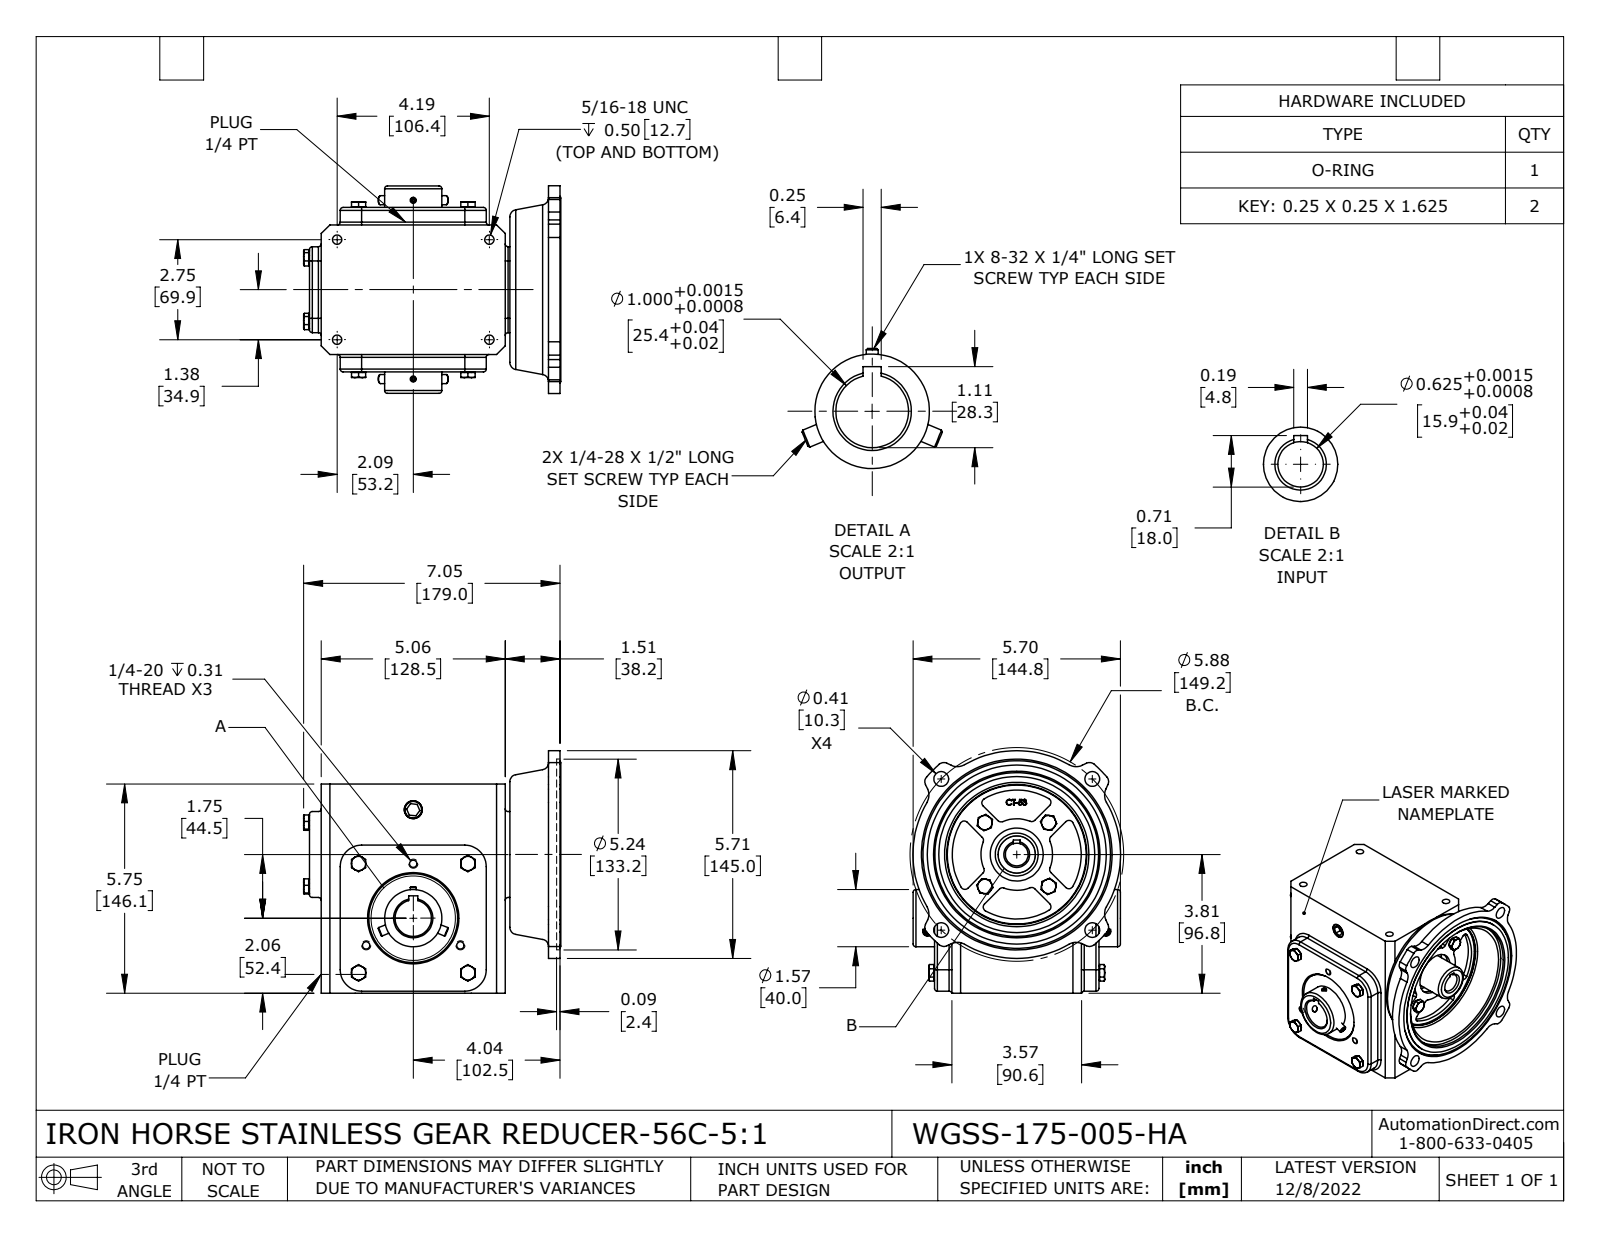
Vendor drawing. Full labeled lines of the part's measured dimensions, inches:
Part name (STEP PRODUCT): WGSS-175-005-HA
STEP written by: SolidWorks 2021 (CONFIG_CONTROL_DESIGN)
Units: inches
Bodies: 7 solids, 891 faces (390 planar, 231 cylindrical, 270 other)
Overall size (bounding box): 7.071 × 6.691 × 5.709
Volume: 127 in³ · Surface area: 281 in²
Round holes (diameter × count): ⌀0.213 ×4, ⌀0.257 ×4, ⌀0.406 ×4, ⌀0.201 ×3, ⌀0.136 ×2, ⌀0.625 ×1, ⌀0.866 ×1, ⌀1 ×1, ⌀1.102 ×1, ⌀1.457 ×1, ⌀1.575 ×1, ⌀3.819 ×1
Round bosses / shafts (diameter × count): ⌀0.394 ×8, ⌀0.25 ×4, ⌀0.164 ×2, ⌀4.921 ×1, ⌀2.441 ×1, ⌀1.575 ×1, ⌀1.181 ×1
Partial cylindrical surfaces — rounded edges, fillets, slot ends (radius × count): R0.079 ×28, R0.118 ×16, R0.394 ×12, R0.197 ×8, R0.591 ×4, R0.984 ×1, R1.772 ×1, R2.854 ×1
Main face-to-face distances: 0.48, 4.04, 5.75, 5.06, 0.157, 3.56, 4.52, 0.315, 6.565, 1.506
Hole centre spacings: 2.357, 2.937, 4.154, 1.496, 2.591, 4.913, 2.75, 4.188
